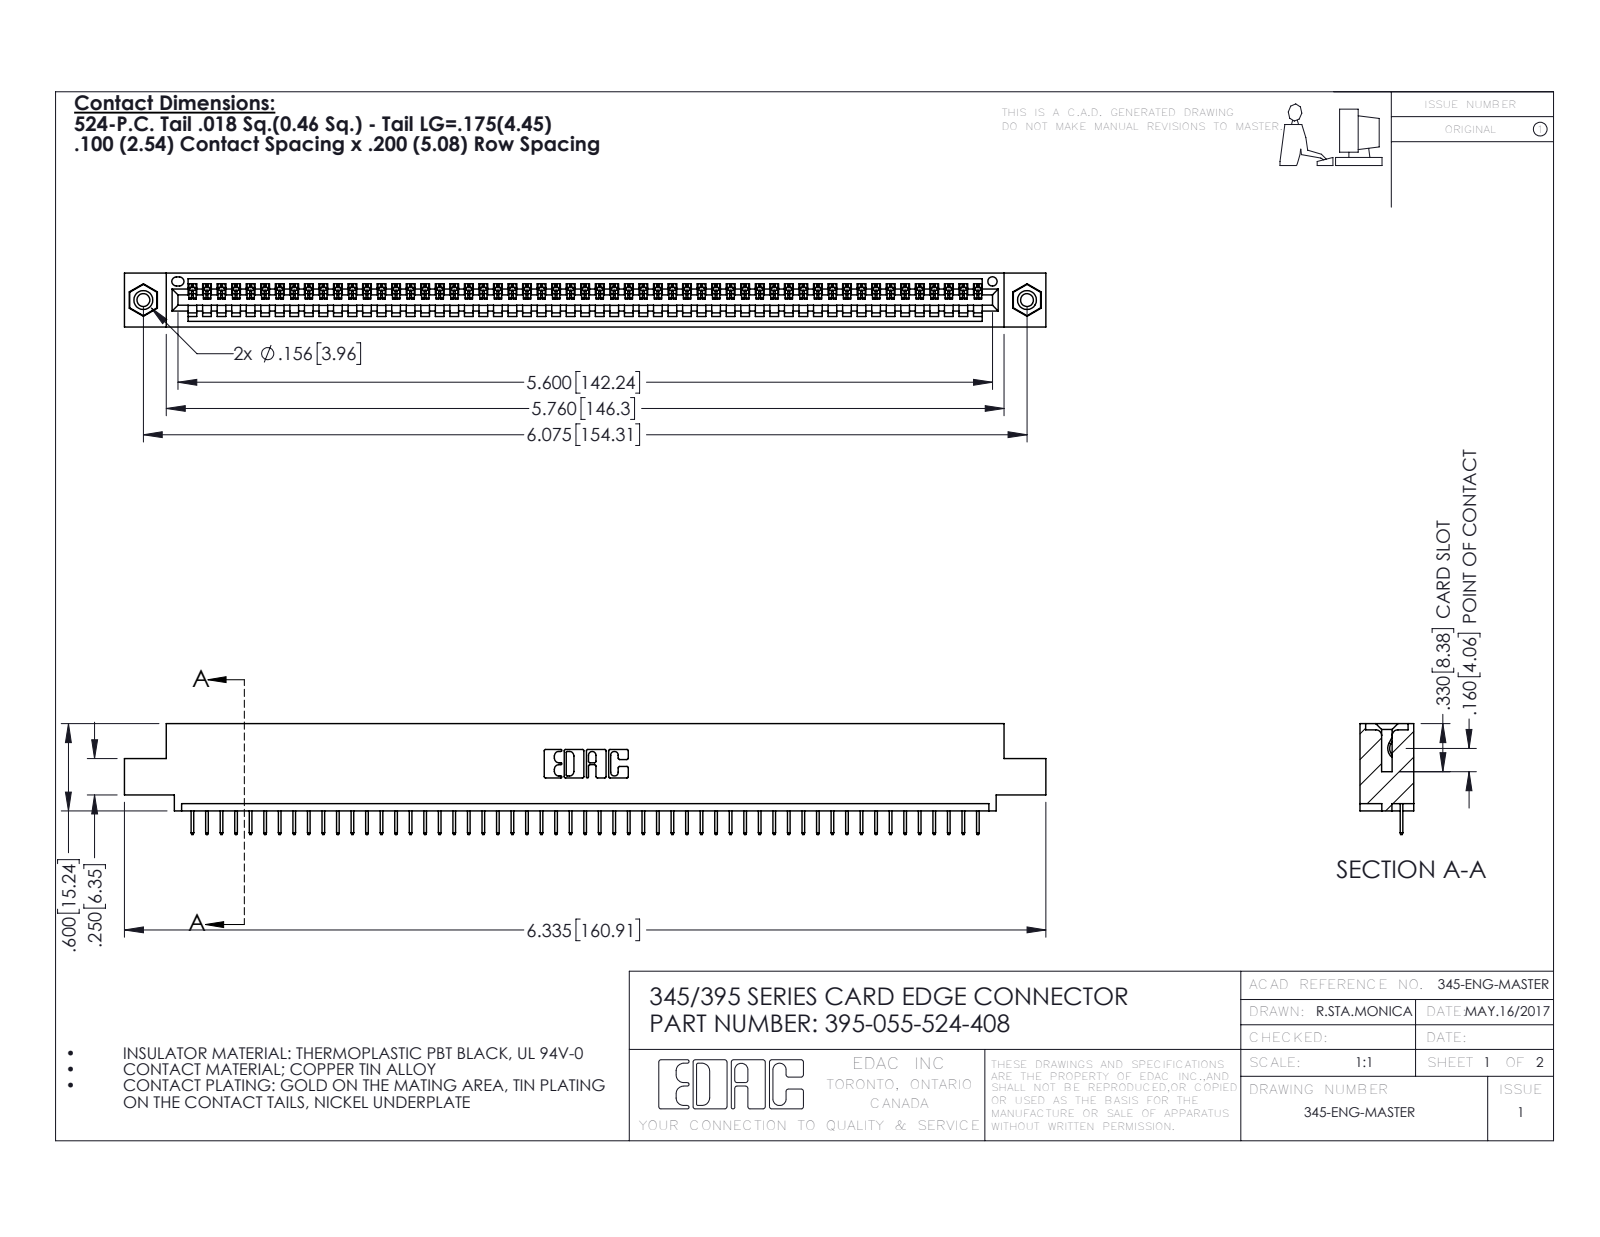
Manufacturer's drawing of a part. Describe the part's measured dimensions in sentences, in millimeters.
The part is named "345-250-001_345-250-003-102; 345-292-001_345-293-124; 395-055-524-408; 345 Part_0.110 Offset - 0.156 Dia-TI". Its 3-D file was written by "SolidWorks 2016 (CONFIG_CONTROL_DESIGN)". It is 58 solids with 3600 faces: 2646 planar, 938 cylindrical and 16 other. Overall it measures 160.9 by 19.4 by 9.4 millimeters. Its volume is 15 100 cubic millimeters and its surface area 19 640 square millimeters. Round holes: 2 of diameter 2.3, 2 of diameter 3.2, 2 of diameter 4, 1 of diameter 1.6. Round bosses or shafts: 2 of diameter 3.9. Partial cylindrical surfaces (rounded edges, fillets, slot ends): 110 of radius 0.2, 22 of radius 0.3, 6 of radius 0.2, 6 of radius 0.8, 3 of radius 0.7, 2 of radius 0.8, 2 of radius 1, 1 of radius 0.4. The main face-to-face distances are 1.8, 7.6, 9.4, 5.1, 2.5, 6.9, 0.6, 5.7, 1.8, 3.8. The hole center spacings are 6.9, 148.3, 154.3.
